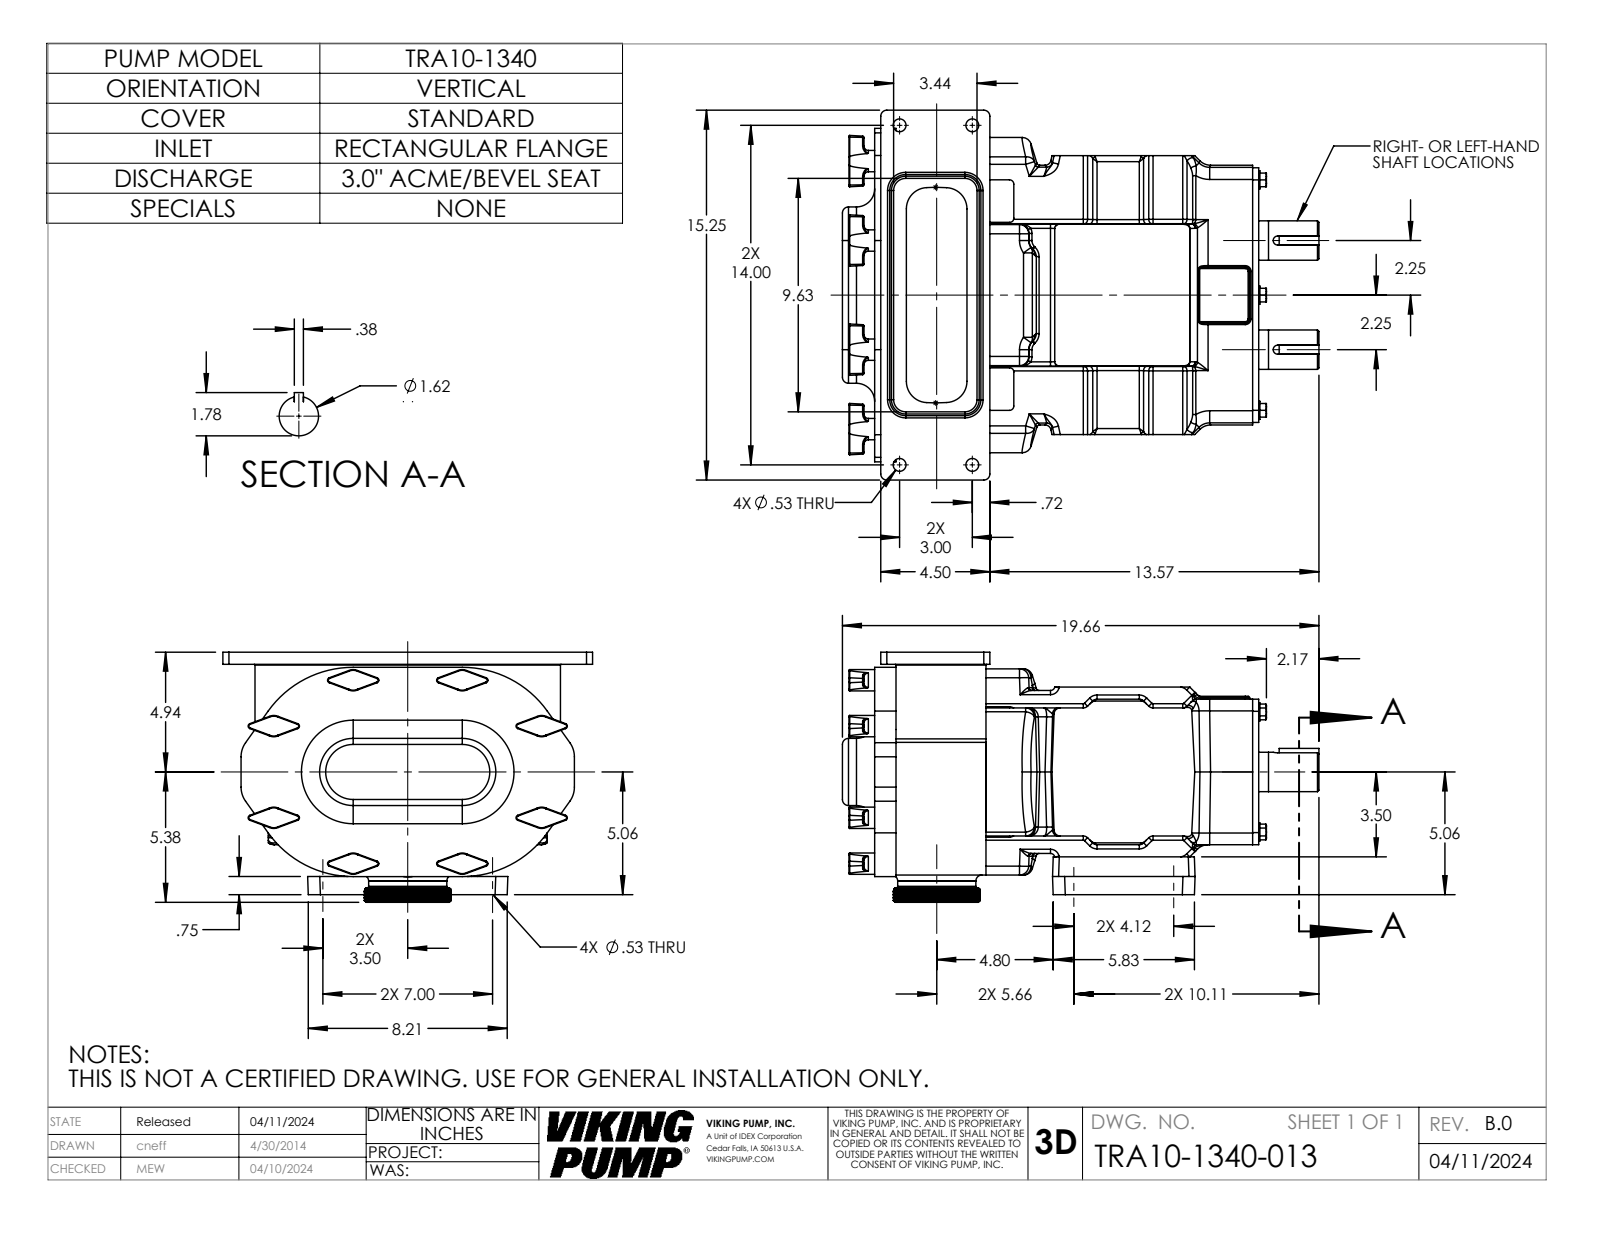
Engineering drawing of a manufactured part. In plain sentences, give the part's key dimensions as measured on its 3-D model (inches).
The part is named "TRA10-0600-GEARBOX-V; TRA10-1340-BODY; 1300IMDA30; TRA10-1340-013 (+1 more)". Its 3-D file was written by "SolidWorks 2022 (AUTOMOTIVE_DESIGN)". It is 4 solids with 1115 faces: 298 planar, 413 cylindrical and 404 other. Overall it measures 19.656 by 15.25 by 10.313 inches. Its volume is 1 334 cubic inches and its surface area 1 462 square inches. Round holes: 8 of diameter 0.531, 1 of diameter 2.868. Round bosses or shafts: 8 of diameter 0.88, 6 of diameter 0.75, 2 of diameter 1.624, 1 of diameter 3.586, 1 of diameter 3.441, 1 of diameter 3.224. Partial cylindrical surfaces (rounded edges, fillets, slot ends): 44 of radius 0.18, 43 of radius 0.06, 36 of radius 0.03, 36 of radius 0.25, 28 of radius 0.38, 26 of radius 0.5, 24 of radius 0.12, 16 of radius 0.09. The main face-to-face distances are 3.711, 0.25, 0.88, 4.591, 0.5, 0.36, 15.841, 14.961, 11.25, 1.437. The hole center spacings are 3, 4.12, 5.458, 6.651, 7, 7.152, 7.166, 7.995.
